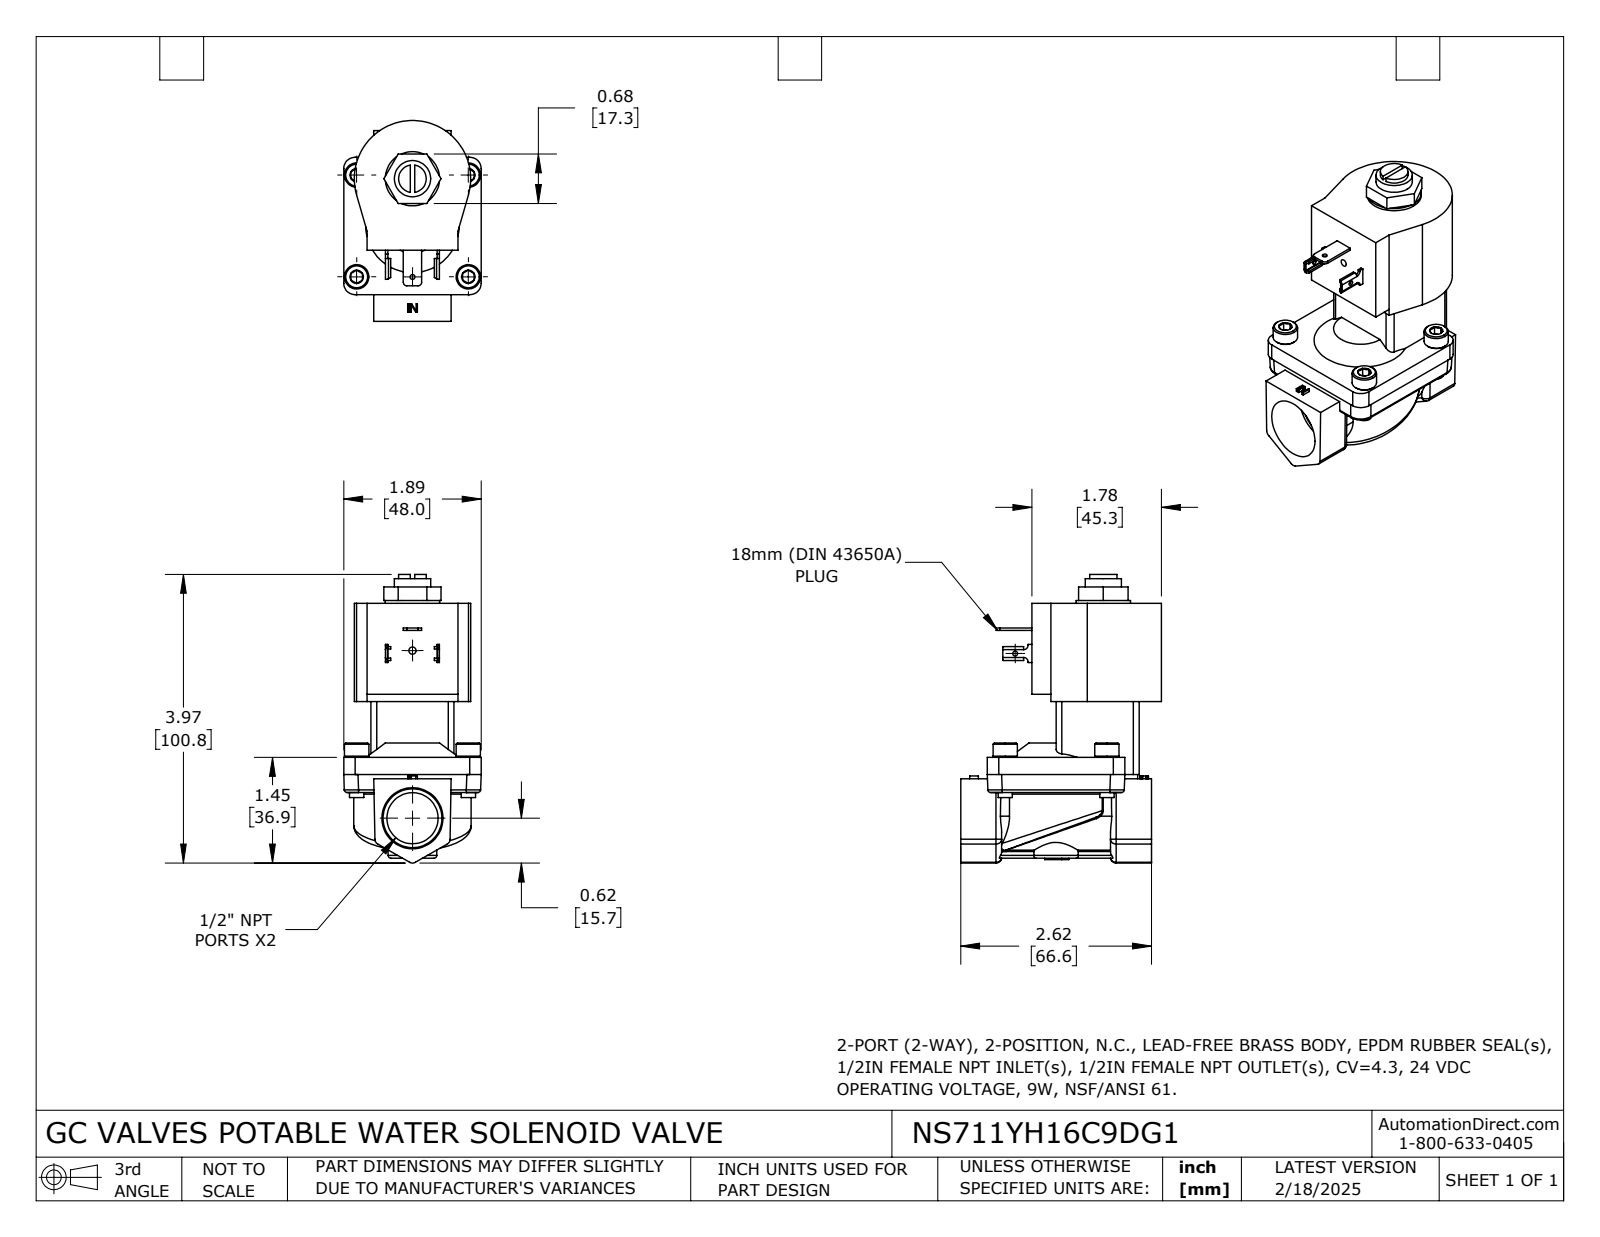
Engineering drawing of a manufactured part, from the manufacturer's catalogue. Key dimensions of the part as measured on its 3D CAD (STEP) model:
Part name (STEP PRODUCT): NS711YH16C9DG1
STEP written by: SolidWorks 2024 (CONFIG_CONTROL_DESIGN)
Units: millimetres
Bodies: 1 solid, 486 faces (270 planar, 113 cylindrical, 103 other)
Overall size (bounding box): 100.77 × 70.12 × 48
Volume: 127 340 mm³ · Surface area: 26 767 mm²
Round holes (diameter × count): ⌀1.68 ×1, ⌀1.7 ×1, ⌀2.53 ×1, ⌀17.86 ×1, ⌀30.48 ×1
Round bosses / shafts (diameter × count): ⌀8.5 ×4, ⌀5 ×4, ⌀18.95 ×1, ⌀12.67 ×1, ⌀9.65 ×1
Partial cylindrical surfaces — rounded edges, fillets, slot ends (radius × count): R2 ×15, R0.5 ×6, R1 ×6, R0.15 ×4, R1.04 ×4, R4 ×4, R5 ×4, R1.27 ×2
Main face-to-face distances: 19.5, 34.29, 53.79, 29, 22.04, 2.54, 31.75, 33.3, 37.44, 9.5
Hole centre spacings: 34.29, 58.5
